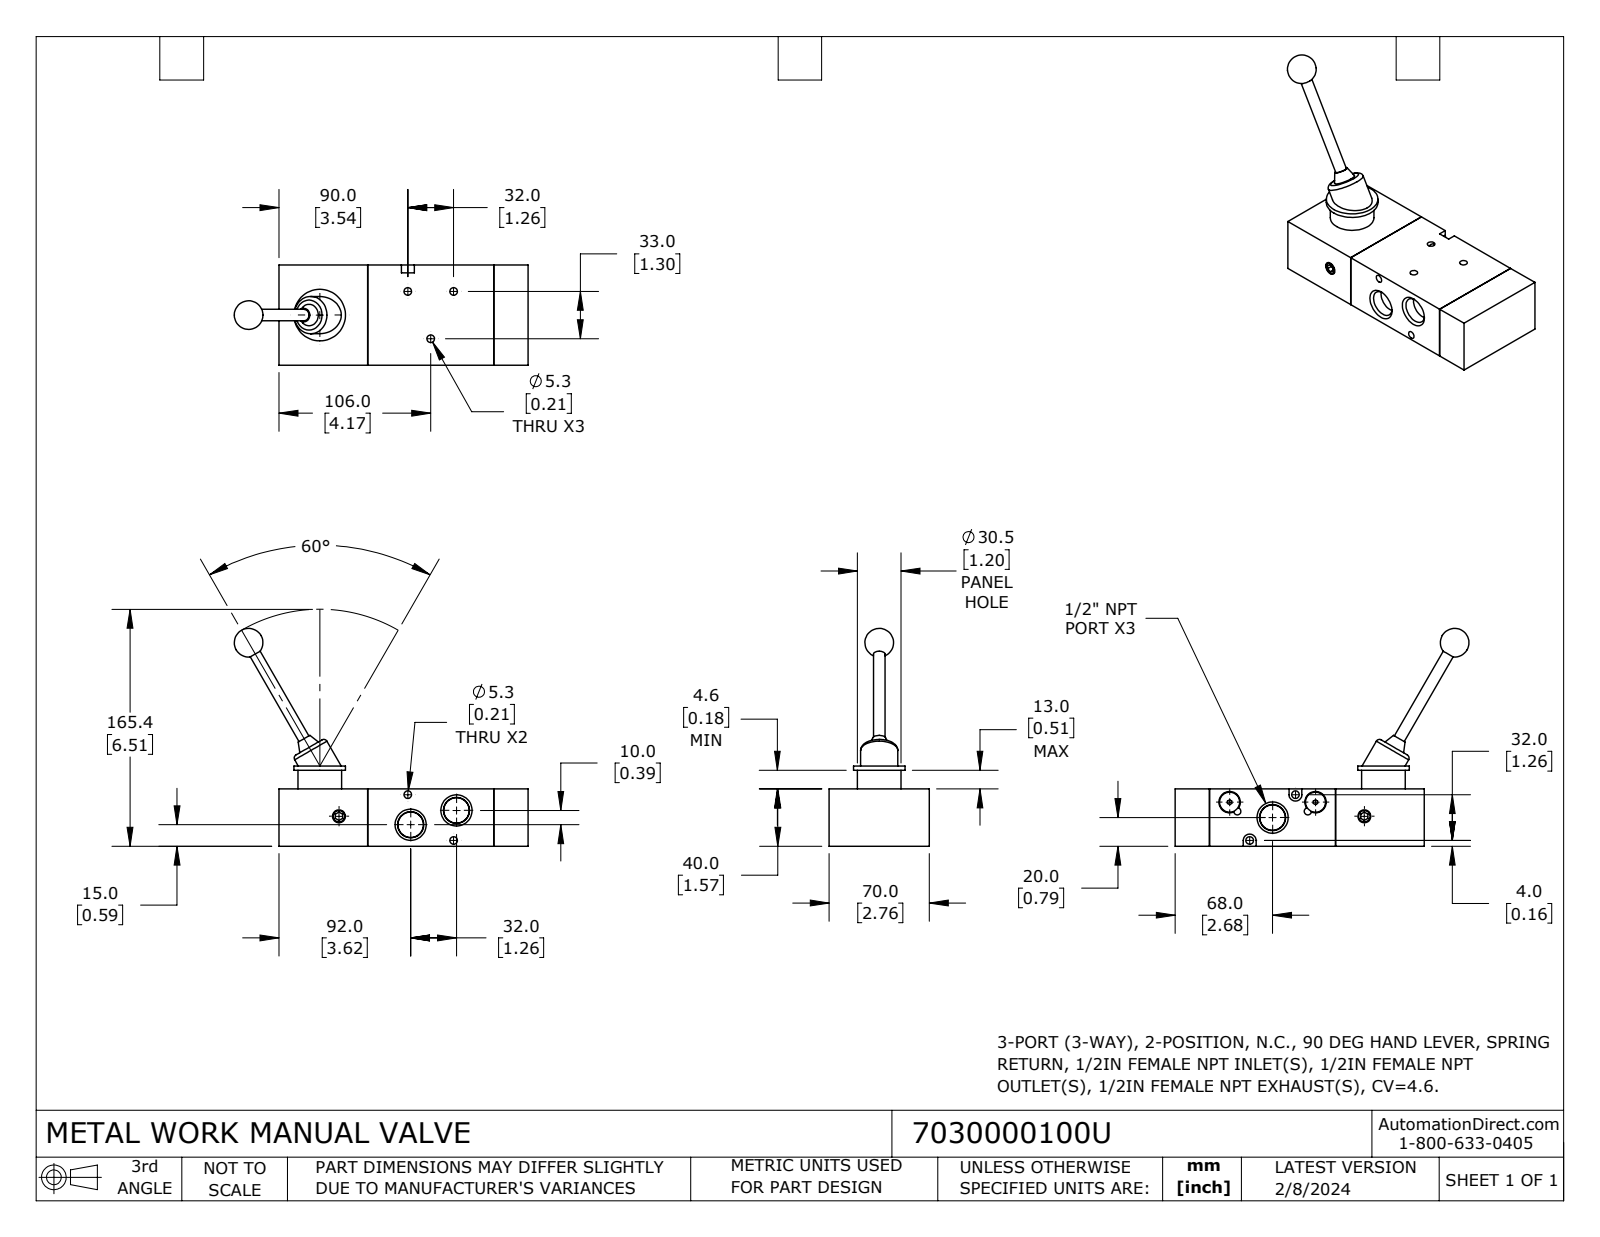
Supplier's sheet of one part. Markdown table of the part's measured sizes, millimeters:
| quantity | value |
| --- | --- |
| part name | 7030000100U |
| STEP written by | SolidWorks 2023 (CONFIG_CONTROL_DESIGN) |
| units | millimeters |
| bodies | 3 solids, 136 faces (67 planar, 51 cylindrical, 18 other) |
| overall size | 205.2 × 152.1 × 70 |
| volume | 501 900 mm³ |
| surface area | 68 260 mm² |
| round holes (diameter × count) | 5.3 × 5, 14.9 × 2, 9 × 1 |
| round bosses / shafts (diameter × count) | 14 × 2, 36 × 1, 30.5 × 1, 26 × 1, 8 × 1, 8 × 1 |
| partial cylindrical surfaces (radius × count) | 2.5 × 2, 4.5 × 2 |
| main face-to-face distances | 40, 70, 88, 24, 112, 174, 150, 62, 9, 61 |
| hole center spacings | 36.7, 15, 30.2, 32, 35.5, 45.2, 46.3, 50.4 |
